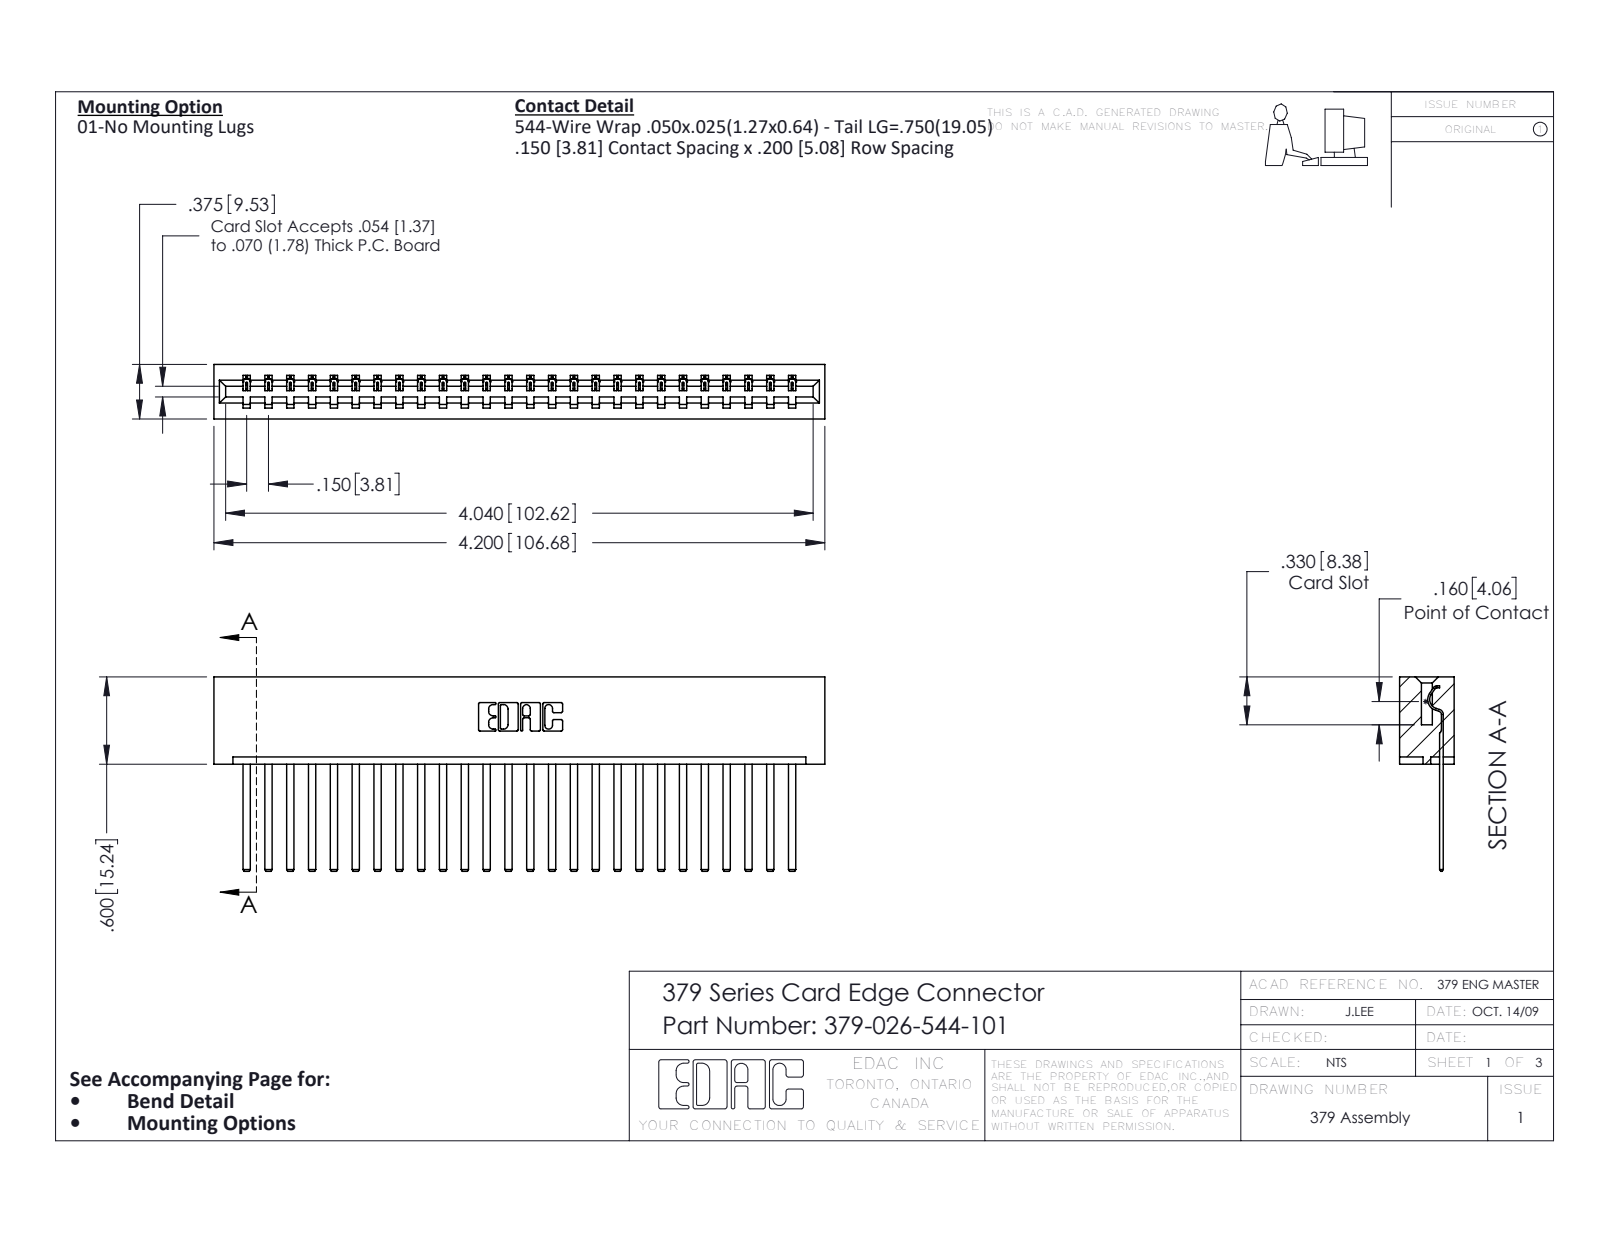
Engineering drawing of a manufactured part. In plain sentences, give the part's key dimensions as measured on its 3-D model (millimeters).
The part is named "379-026-544-101; 379 Part_Lugless; 345-292-001_345-293-144". Its 3-D file was written by "SolidWorks 2016 (CONFIG_CONTROL_DESIGN)". It is 27 solids with 1458 faces: 1054 planar, 404 cylindrical and 0 other. Overall it measures 106.7 by 34 by 9.5 millimeters. Its volume is 12 000 cubic millimeters and its surface area 13 200 square millimeters. Partial cylindrical surfaces (rounded edges, fillets, slot ends): 52 of radius 0.2, 22 of radius 0.3, 6 of radius 0.2, 6 of radius 0.8, 3 of radius 0.7, 1 of radius 0.4, 1 of radius 0.6, 1 of radius 0.6. The main face-to-face distances are 7.6, 1.9, 9.5, 2.5, 7, 0.6, 15.2, 5.7, 3.8, 11.4.
